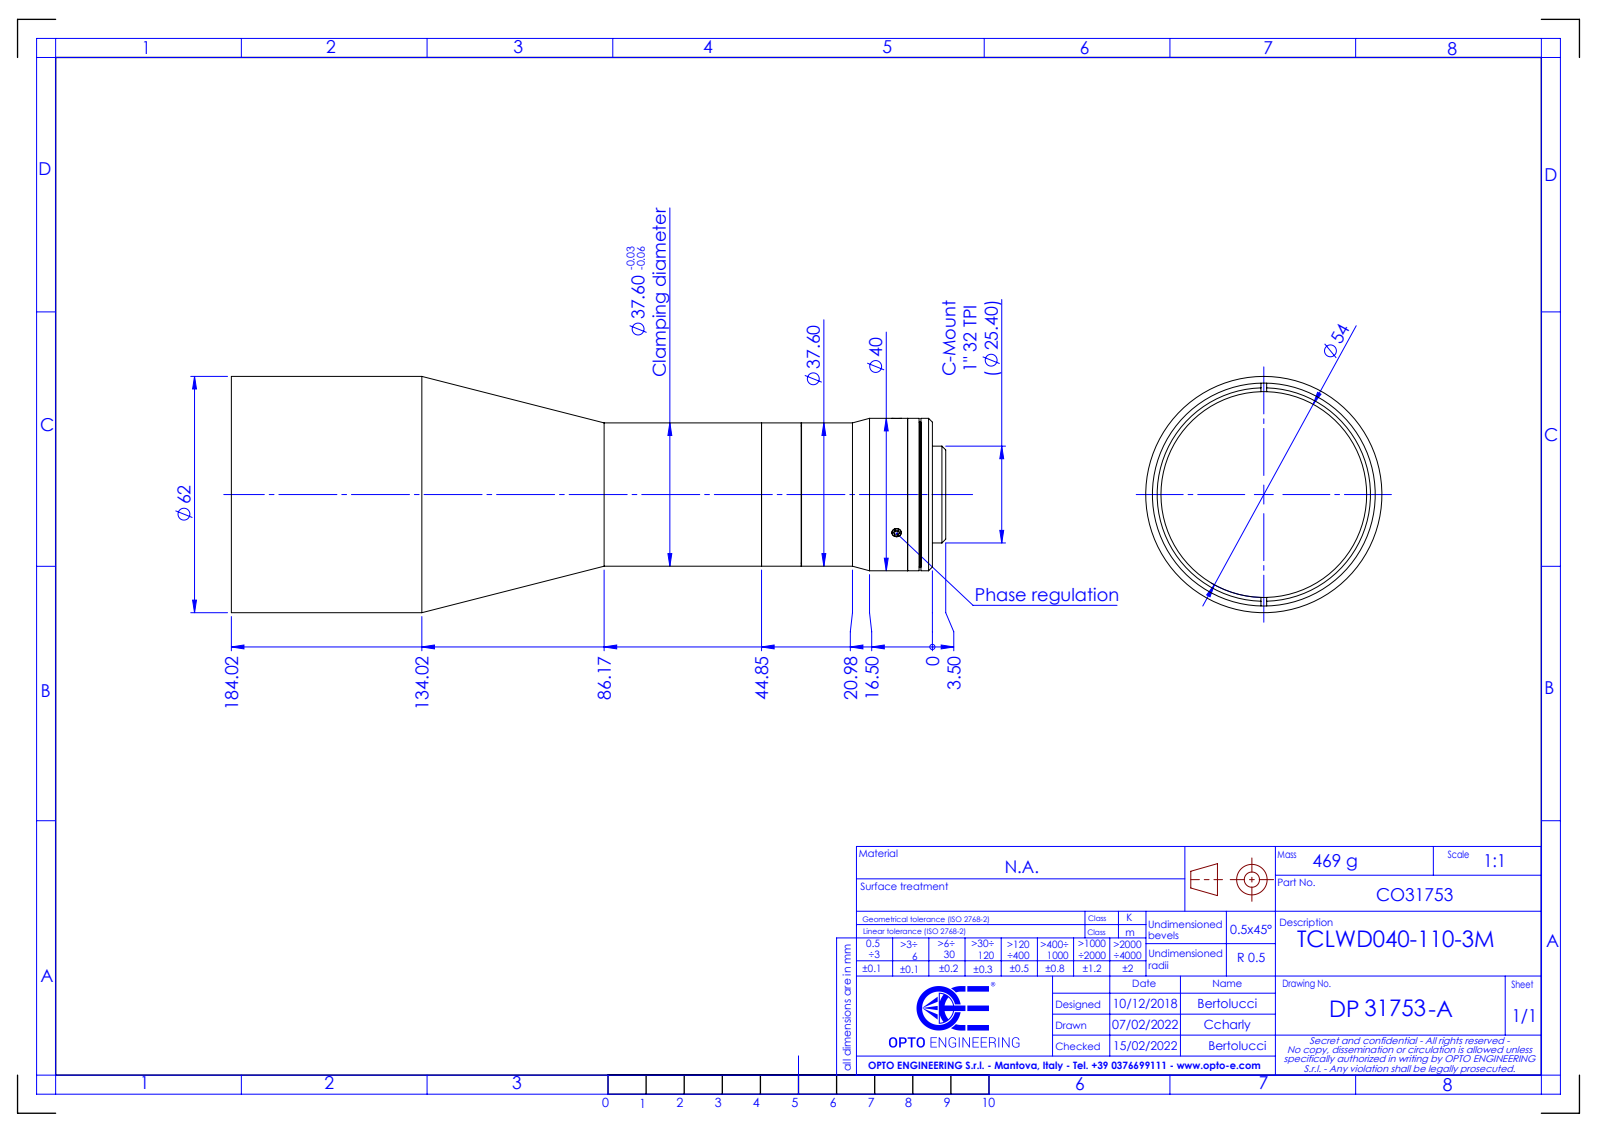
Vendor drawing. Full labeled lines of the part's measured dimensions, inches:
Part name (STEP PRODUCT): DP31753-A_TCLWD040-110-3M
STEP written by: SolidWorks 2021 (CONFIG_CONTROL_DESIGN)
Units: inches
Bodies: 0 solids, 81 faces (36 planar, 24 cylindrical, 21 other)
Overall size (bounding box): 7.383 × 2.441 × 2.441
Round holes (diameter × count): ⌀0.886 ×1, ⌀1.004 ×1, ⌀2.126 ×1, ⌀2.303 ×1
Round bosses / shafts (diameter × count): ⌀2.441 ×1, ⌀1.575 ×1, ⌀1.48 ×1, ⌀1 ×1
Main face-to-face distances: 0.138, 0.118, 0.02, 1.214, 1.234, 1.352, 0.256, 1.096, 5.886, 6.982
